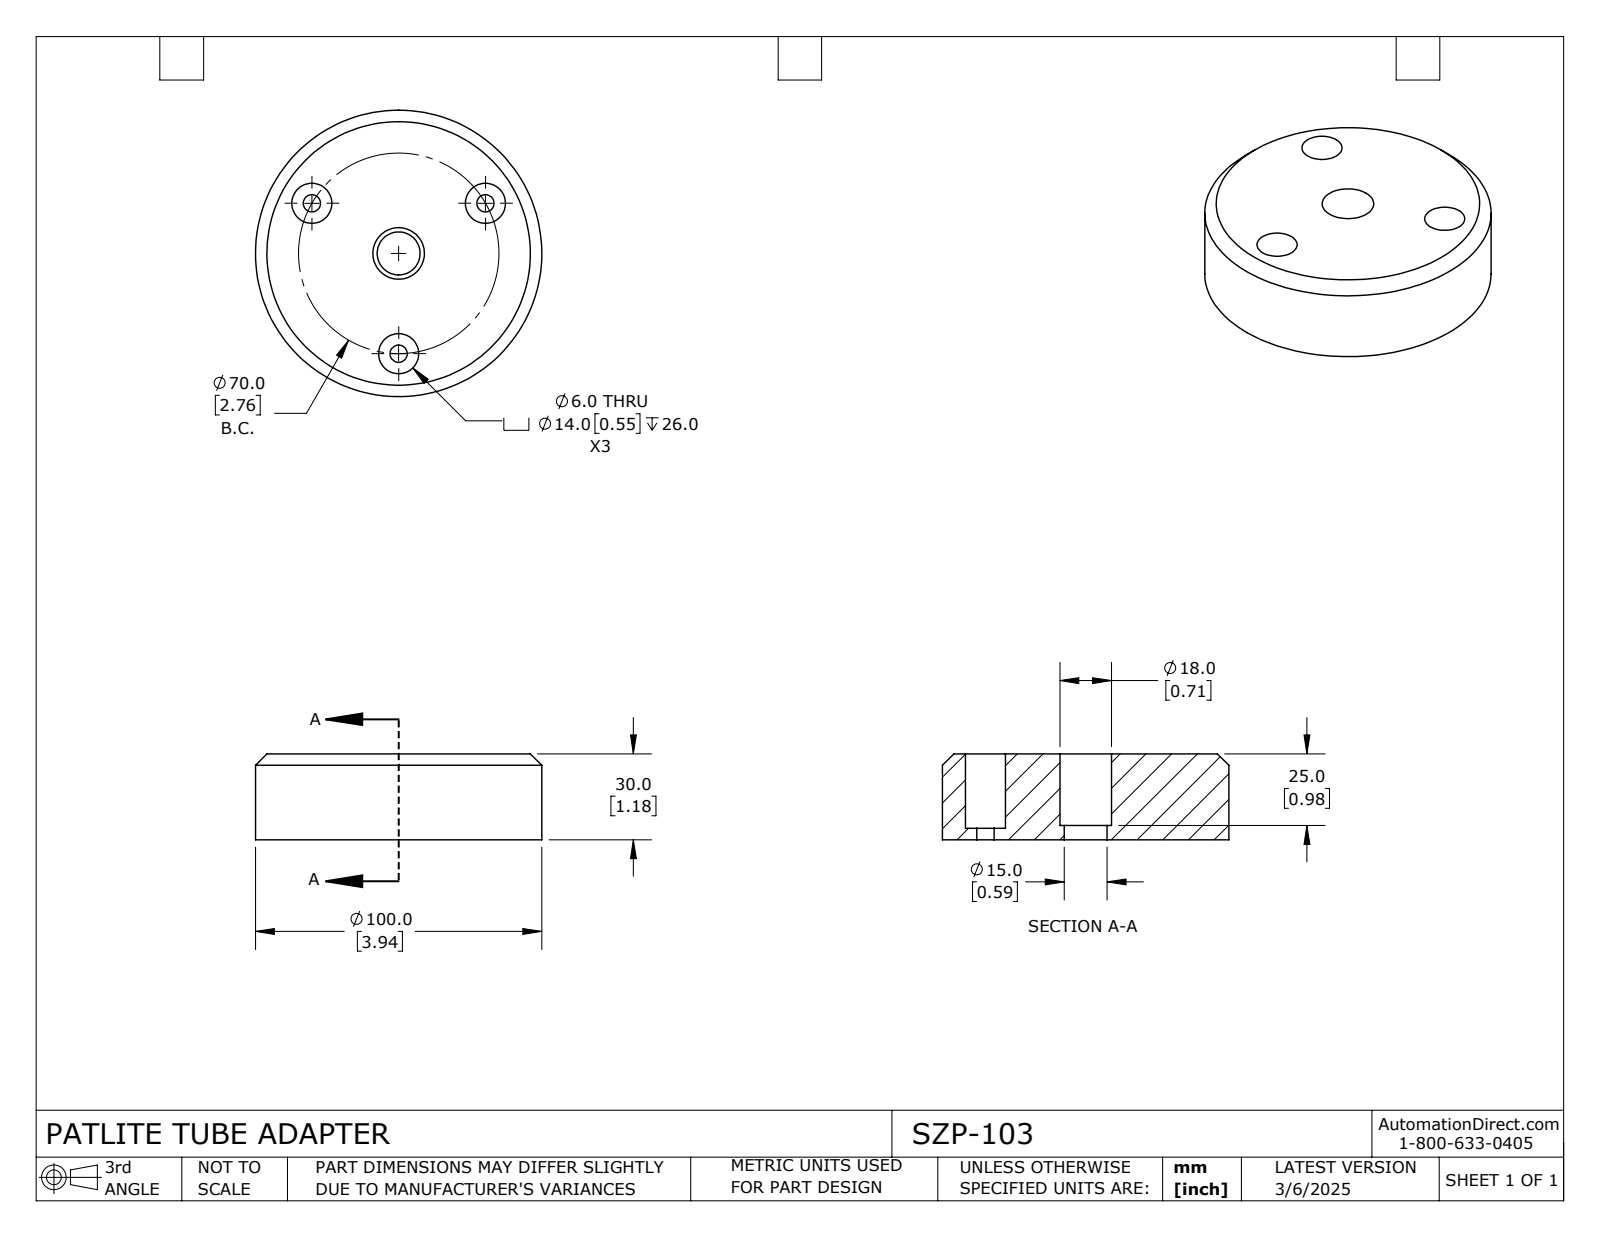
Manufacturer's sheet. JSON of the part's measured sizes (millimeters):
{"part_name": "SZP-103", "step_written_by": "SolidWorks 2024 (CONFIG_CONTROL_DESIGN)", "units": "millimeters", "bodies": {"solids": 1, "faces": 32, "planar": 8, "cylindrical": 22, "other": 2}, "overall_size": [100, 100, 30], "volume_mm3": 212580, "surface_area_mm2": 29952, "round_holes": [[6, 3], [14, 3], [5.05, 2], [15, 1], [18, 1]], "round_bosses_or_shafts": [[100, 1]], "face_to_face_distances": [30, 4, 26, 5, 25, 1, 21, 20], "hole_center_spacings": [35, 60.62, 17.72, 27.5, 44.51, 60.4, 55]}
